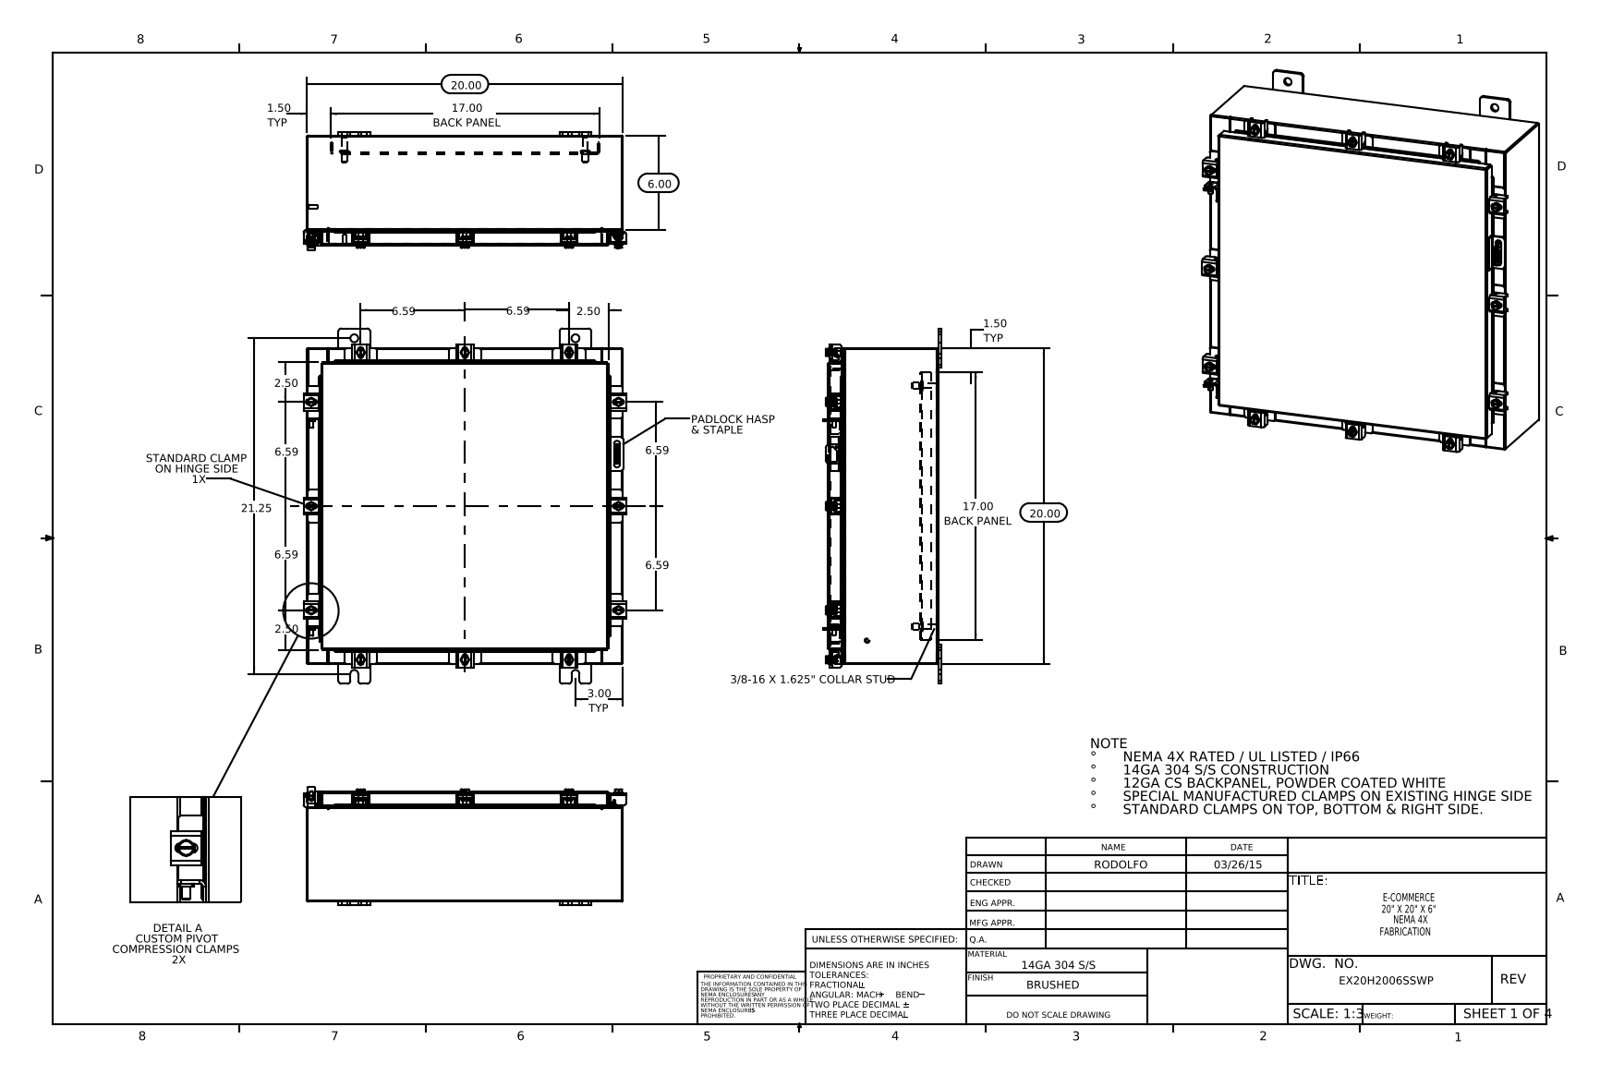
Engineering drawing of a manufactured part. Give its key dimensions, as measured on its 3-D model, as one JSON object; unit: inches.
{"part_name": "EX20H2006SSWP Special Clamp; EX20H2006SSWP Body; EX20H2006SSWP Bottom; EX20H2006SSWP Backpanel (+8 more)", "step_written_by": "SolidWorks 2014 (CONFIG_CONTROL_DESIGN)", "units": "inches", "bodies": {"solids": 81, "faces": 2018, "planar": 1075, "cylindrical": 783, "other": 160}, "overall_size": [22.5, 20.421, 7.453], "volume_in3": 149.7, "surface_area_in2": 3735, "round_holes": [[0.213, 12], [0.26, 12], [0.5, 8], [0.125, 1], [0.25, 1]], "round_bosses_or_shafts": [[0.5, 12], [0.25, 12], [0.399, 10], [0.625, 4], [0.375, 4], [0.33, 4], [0.315, 2], [0.236, 2]], "partial_cylinders_radius": [[0.06, 54], [0.013, 24], [0.141, 24], [0.19, 24], [0.088, 22], [0.12, 22], [0.09, 18], [0.05, 17]], "face_to_face_distances": [0.075, 6.9, 19.925, 6.975, 6.826, 0.104, 1, 1.075, 5.826, 5.9], "hole_center_spacings": [6.594, 10.217, 16.617, 18.998, 20.539, 2.34, 14.374, 17.381]}
